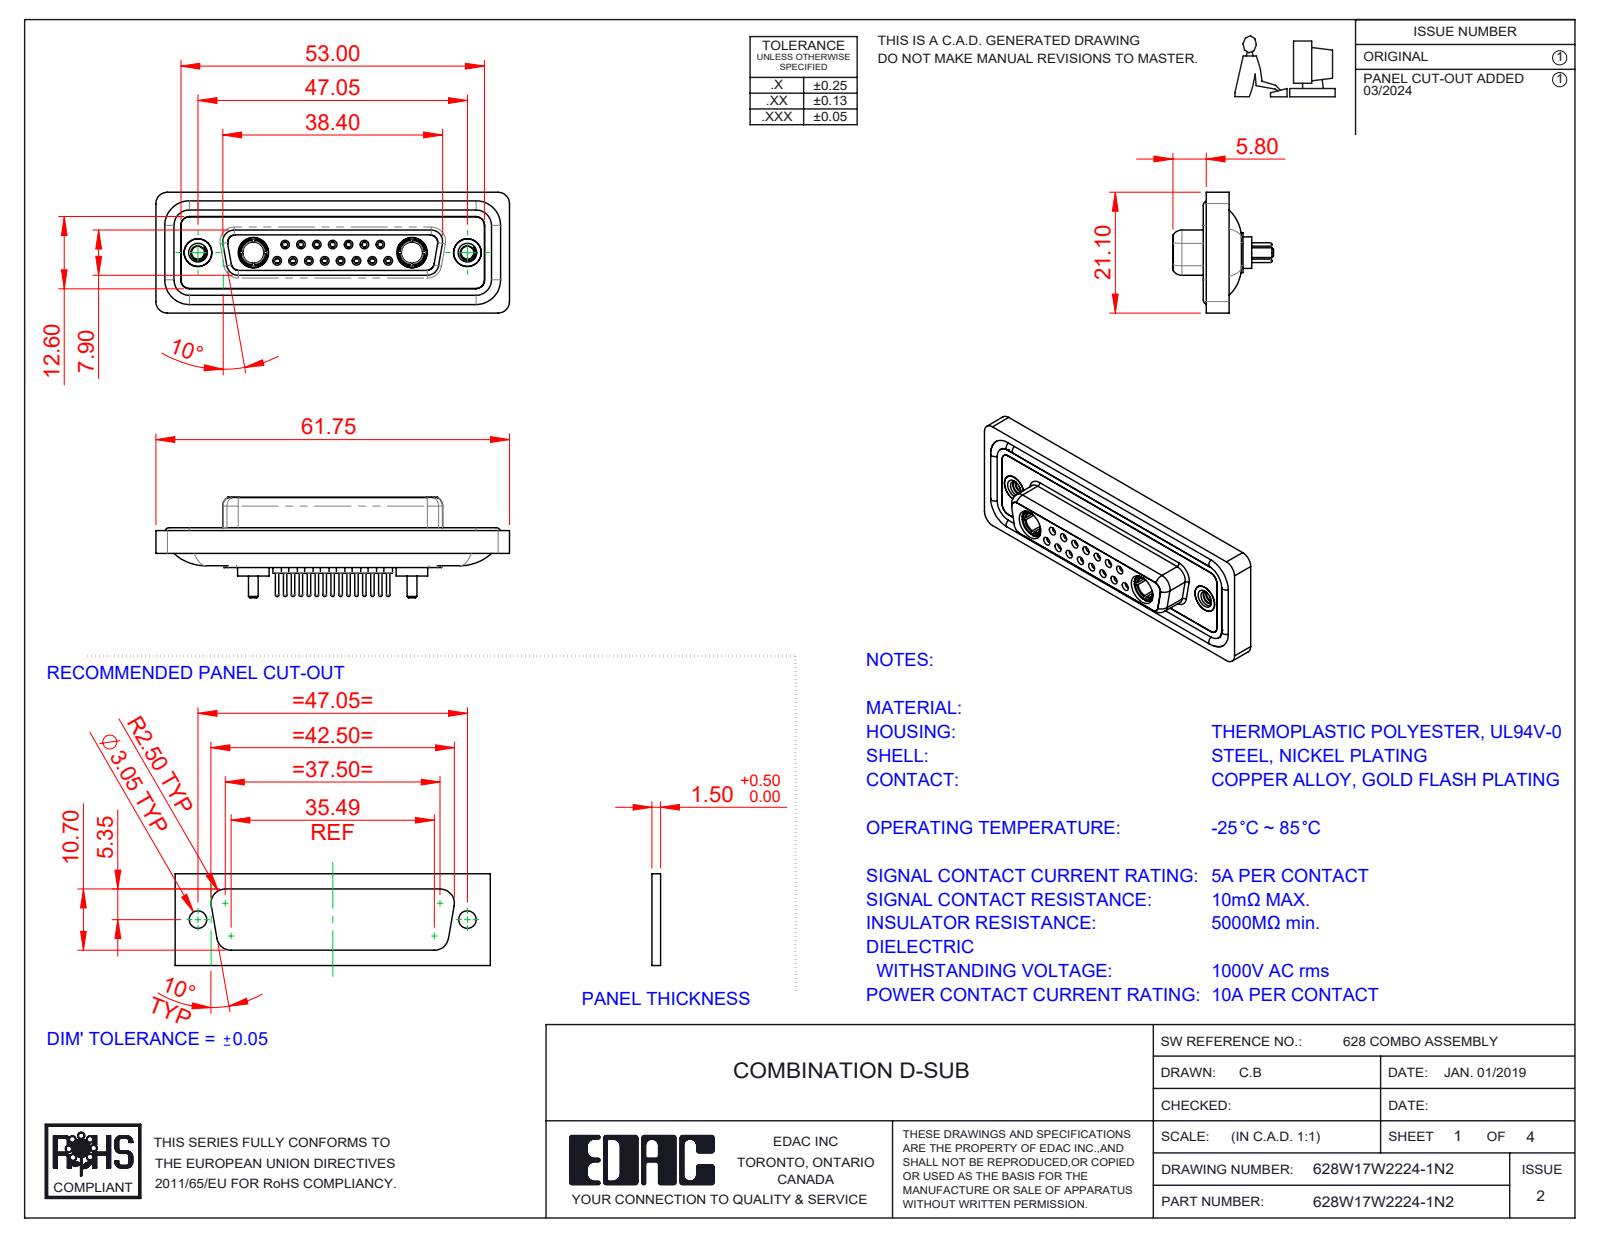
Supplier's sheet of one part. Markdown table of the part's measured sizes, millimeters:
| quantity | value |
| --- | --- |
| part name | 628Combo Contact Row 2_24; 628Combo Housing_17W2; 628W17W2224-1N2; Power Socket_10A S (+5 more) |
| STEP written by | SolidWorks 2023 (CONFIG_CONTROL_DESIGN) |
| units | millimeters |
| bodies | 26 solids, 1359 faces (388 planar, 519 cylindrical, 452 other) |
| overall size | 61.75 × 21.1 × 17.55 |
| volume | 8 295 mm³ |
| surface area | 13 830 mm² |
| round holes (diameter × count) | 0.9 × 15, 1.1 × 15, 1.5 × 15, 2 × 15, 1.6 × 8, 1.7 × 7, 4.85 × 4, 2.26 × 2, 3.7 × 2, 4 × 2, 4.05 × 2, 5 × 2 |
| round bosses / shafts (diameter × count) | 2.2 × 15, 0.6 × 15, 1.6 × 11, 5.5 × 2, 5.2 × 2, 4.96 × 2, 4.95 × 2, 4.8 × 2 |
| partial cylindrical surfaces (radius × count) | 1.5 × 22, 2 × 18, 1.35 × 8, 1.6 × 8, 0.25 × 4, 0.5 × 4, 0.6 × 4, 0.65 × 4 |
| main face-to-face distances | 0.4, 1.8, 7.45, 5.65, 6.6, 0.5, 7.05, 1.6, 2.9, 1.1 |
| hole center spacings | 3.16, 2.77, 8.31, 5.54, 5.03, 5.04, 7.49, 11.08 |
